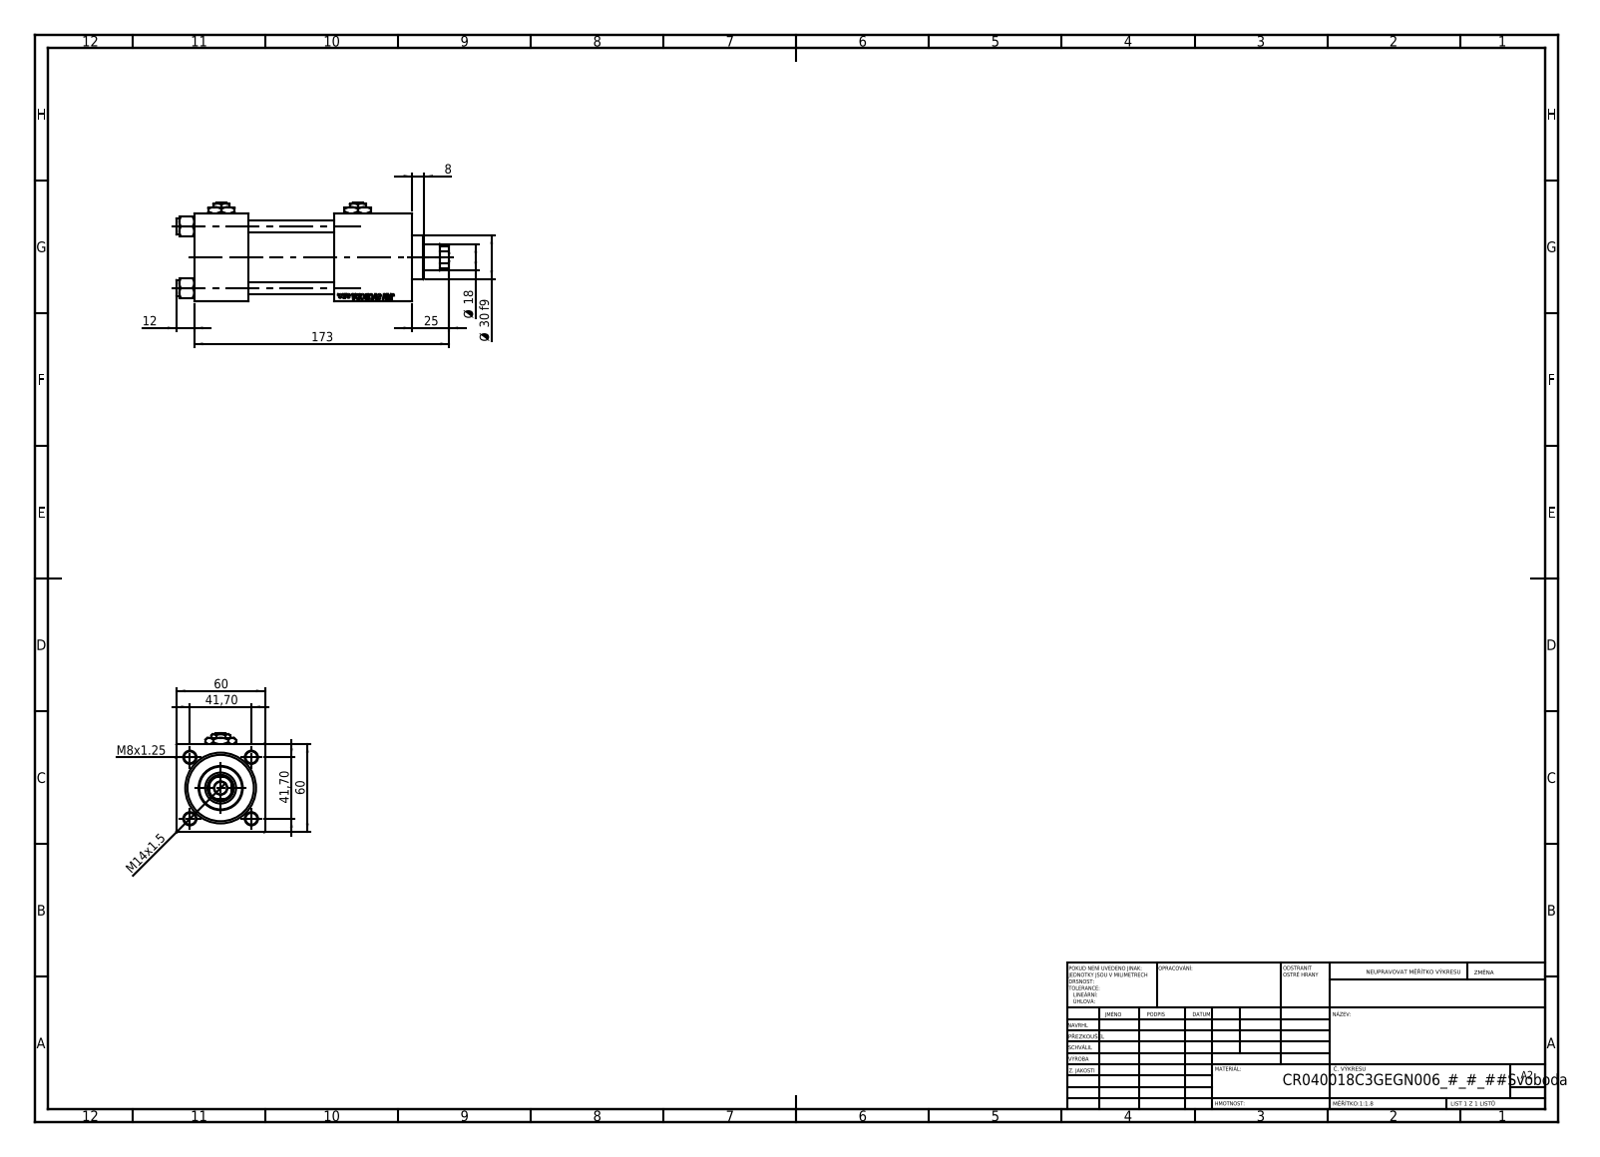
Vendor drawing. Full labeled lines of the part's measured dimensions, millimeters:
Part name (STEP PRODUCT): Zatka_pro_OIL_PORT; V215_VC_A; V215CR_VCP_C; NUT_M5_C (+2 more)
STEP written by: SolidWorks 2019 (CONFIG_CONTROL_DESIGN)
Units: millimetres
Bodies: 13 solids, 1250 faces (574 planar, 98 cylindrical, 578 other)
Overall size (bounding box): 185 × 67 × 60
Volume: 398 841 mm³ · Surface area: 108 335 mm²
Round holes (diameter × count): ⌀8 ×4, ⌀7 ×2, ⌀16.66 ×2, ⌀24 ×2, ⌀8.5 ×1, ⌀18 ×1, ⌀21 ×1, ⌀31 ×1, ⌀40 ×1, ⌀45 ×1
Round bosses / shafts (diameter × count): ⌀11 ×4, ⌀46 ×1, ⌀30 ×1
Partial cylindrical surfaces — rounded edges, fillets, slot ends (radius × count): R8.5 ×1
Main face-to-face distances: 60, 37, 53, 148, 111, 58, 95, 119.3, 82.3, 24.3
Hole centre spacings: 29.49, 41.7, 58.97, 92.5
